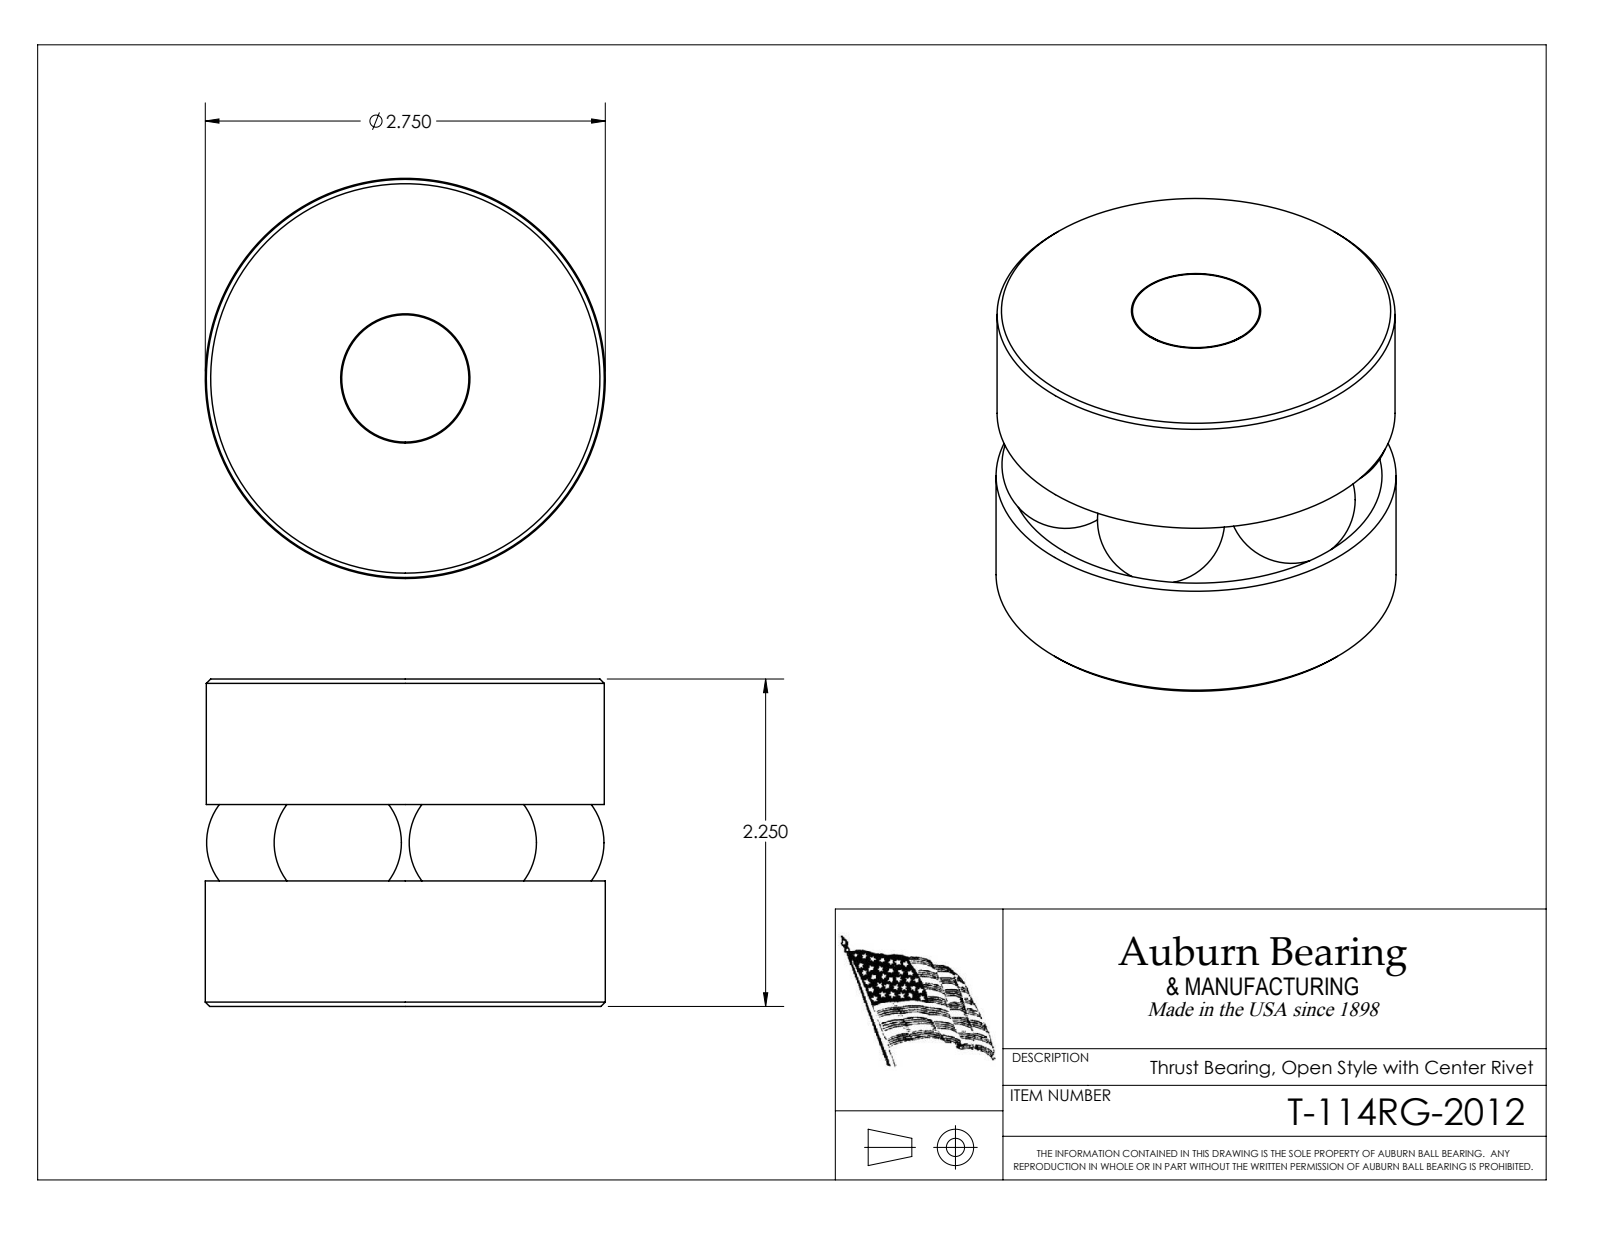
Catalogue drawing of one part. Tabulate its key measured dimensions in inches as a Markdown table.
| quantity | value |
| --- | --- |
| part name | T-114RG_T-114RG-2012 |
| STEP written by | SolidWorks 2016 (CONFIG_CONTROL_DESIGN) |
| units | inches |
| bodies | 9 solids, 27 faces (8 planar, 5 cylindrical, 14 other) |
| overall size | 2.75 × 2.75 × 2.25 |
| volume | 11.32 in³ |
| surface area | 59.56 in² |
| round holes (diameter × count) | 0.322 × 1 |
| round bosses / shafts (diameter × count) | 2.75 × 1, 2.736 × 1, 0.312 × 1 |
| main face-to-face distances | 2.25, 0.863, 1.387, 0.525 |
